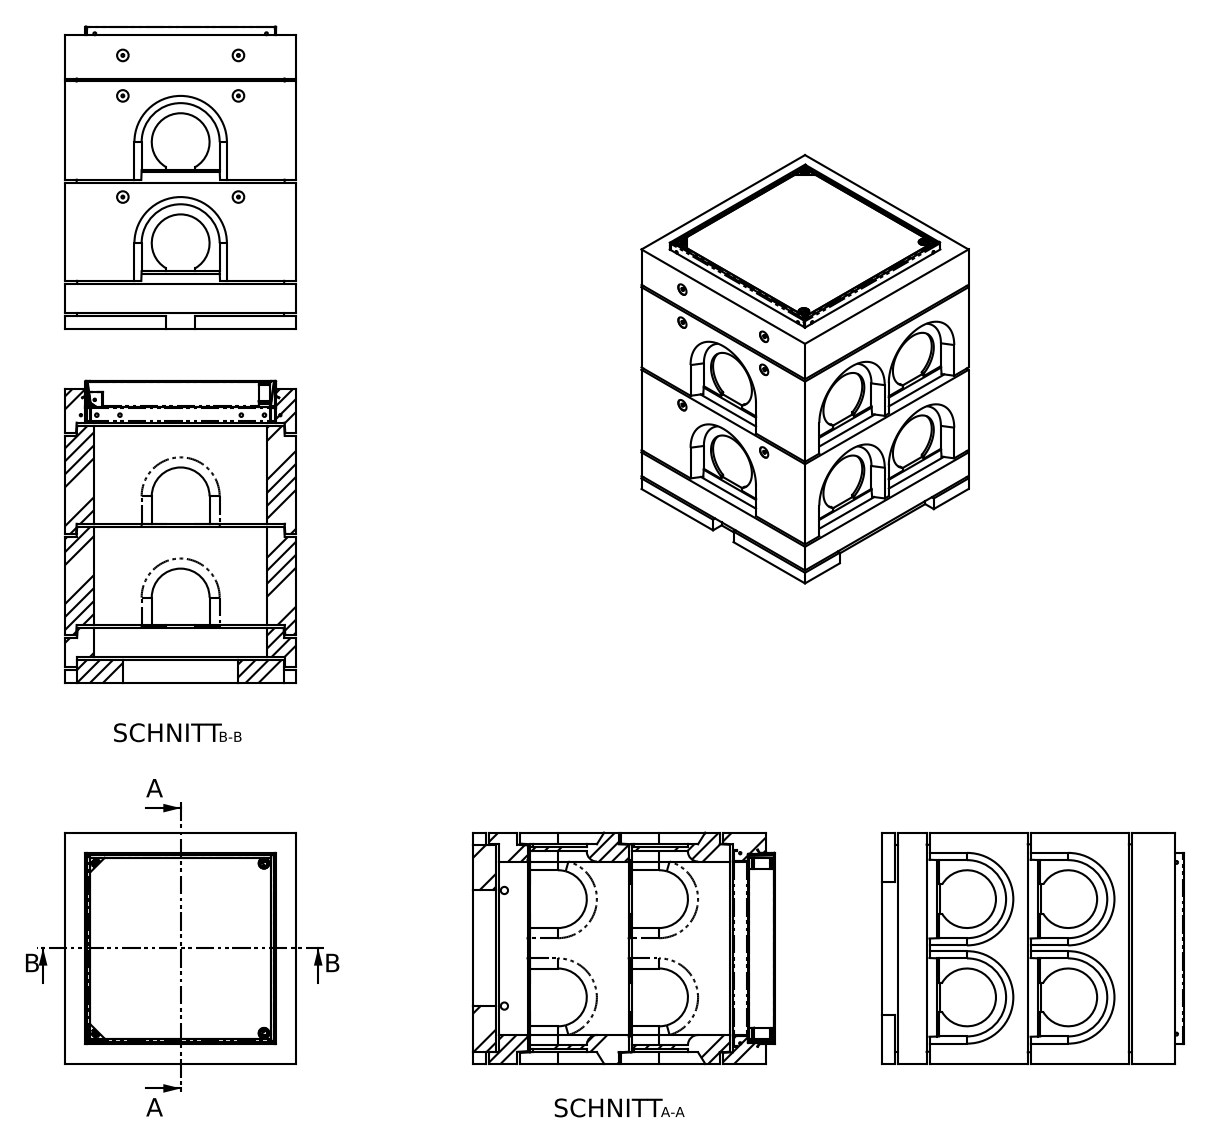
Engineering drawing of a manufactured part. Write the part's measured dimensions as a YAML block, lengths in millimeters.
part_name: "SC-ECO.0606.98.B125.ef"
step_written_by: "SolidWorks 2018 (AUTOMOTIVE_DESIGN)"
units: millimeters
bodies: {solids: 0, faces: 386, planar: 239, cylindrical: 84, other: 63}
overall_size: [1045, 800, 800]
round_holes:
  - {diameter: 200, count: 6}
  - {diameter: 10, count: 4}
  - {diameter: 40, count: 4}
  - {diameter: 26.5, count: 2}
  - {diameter: 35, count: 2}
round_bosses_or_shafts:
  - {diameter: 10, count: 6}
  - {diameter: 5.81, count: 6}
partial_cylinders:
  - {radius: 35, count: 12}
  - {radius: 2.5, count: 4}
  - {radius: 3, count: 4}
  - {radius: 5, count: 4}
  - {radius: 13.5, count: 2}
face_to_face_distances: [800, 700, 100, 10, 35, 25, 50, 350, 685, 600]
hole_center_spacings: [350, 256.12, 235.87, 275.86, 340, 395.92, 400, 478.37]
